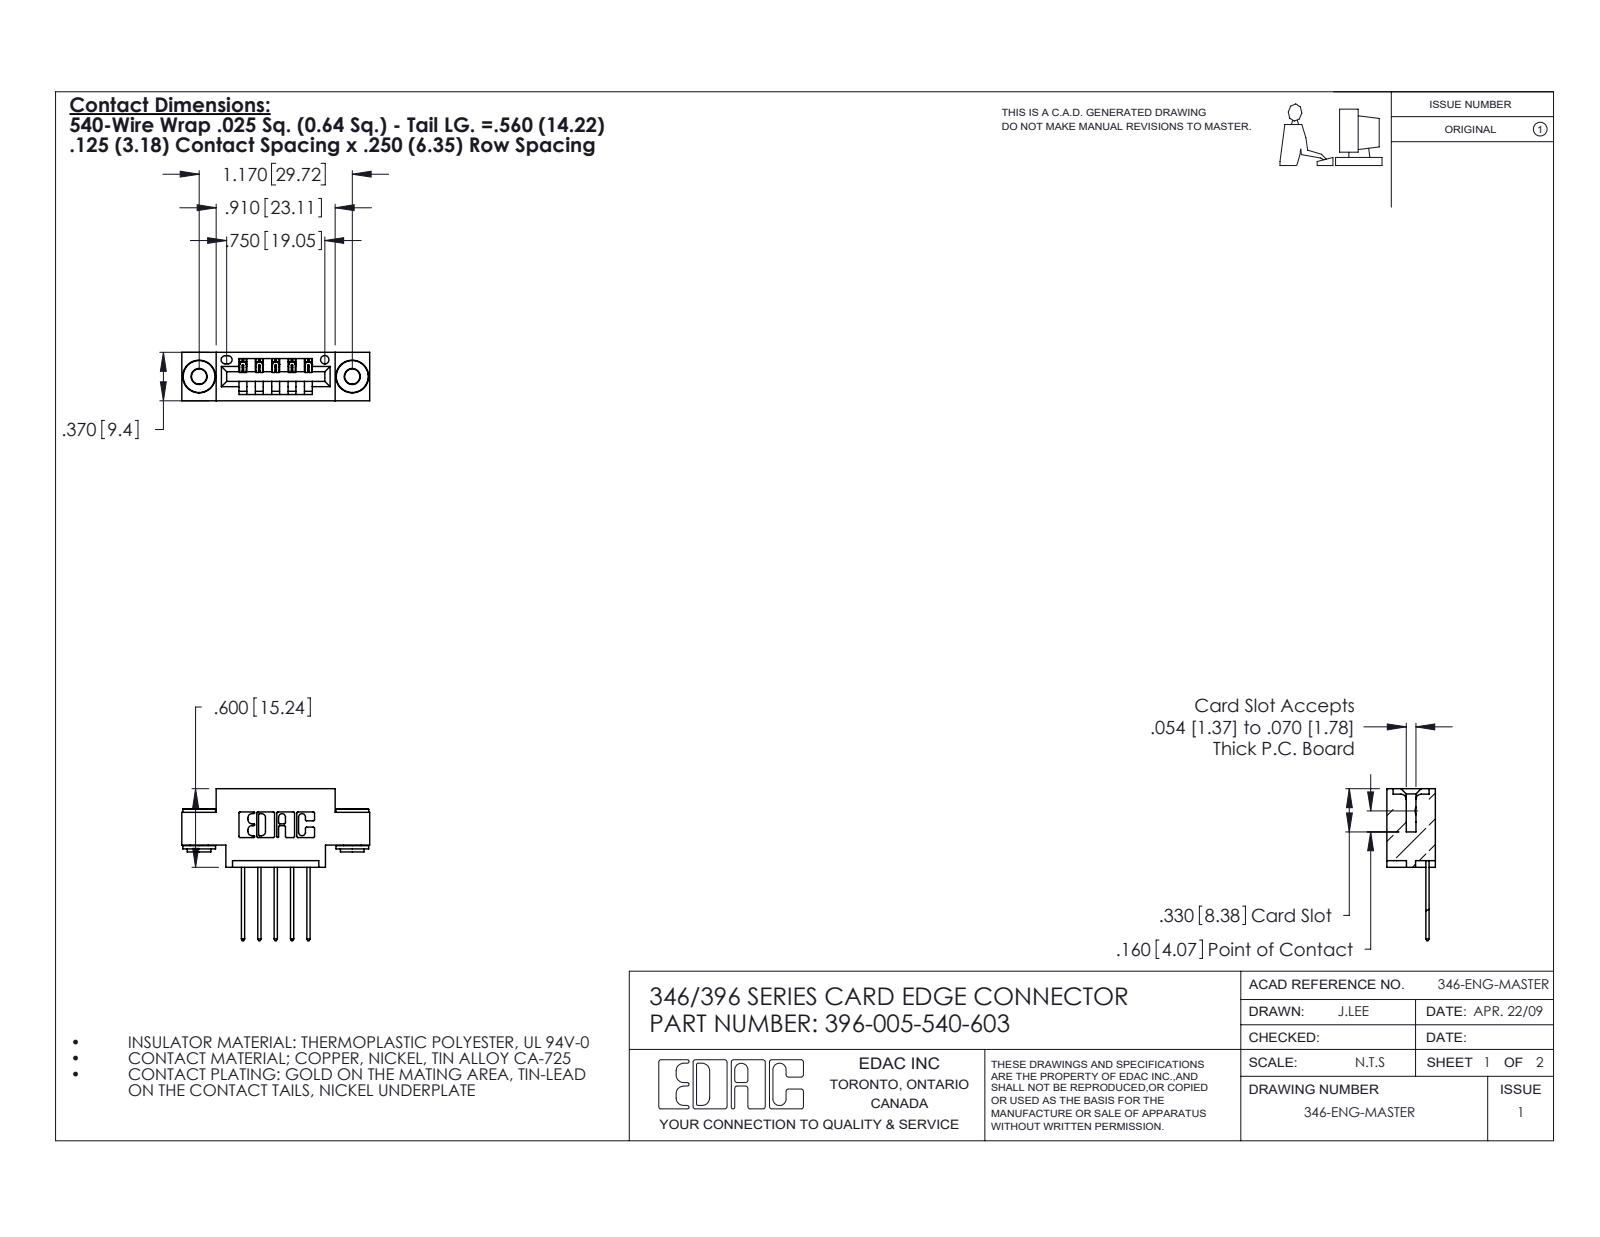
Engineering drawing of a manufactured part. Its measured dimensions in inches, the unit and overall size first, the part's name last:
Units: inches
Overall size (bounding box): 1.435 × 1.16 × 0.37
Round holes (diameter × count): ⌀0.116 ×2, ⌀0.156 ×2, ⌀0.064 ×1
Round bosses / shafts (diameter × count): ⌀0.25 ×2, ⌀0.18 ×2, ⌀0.136 ×2
Partial cylindrical surfaces — rounded edges, fillets, slot ends (radius × count): R0.01 ×22, R0.006 ×10, R0.01 ×10, R0.007 ×6, R0.031 ×6, R0.026 ×3, R0.031 ×2, R0.04 ×2
Main face-to-face distances: 0.25, 0.37, 0.048, 0.322, 0.025, 0.222, 0.072, 0.298, 0.148, 0.1
Hole centre spacings: 0.246, 0.969, 1.17
Volume: 0.188 in³ · Surface area: 6.078 in²
Bodies: 8 solids, 468 faces (304 planar, 156 cylindrical, 8 other)
Part name (STEP PRODUCT): 346 Part_0.170 Offset - 0.156 Dia-TH; 396-005-540-603; 345-292-001_345-293-140; 345-250-002_345-250-002-102
STEP written by: SolidWorks 2020 (CONFIG_CONTROL_DESIGN)
